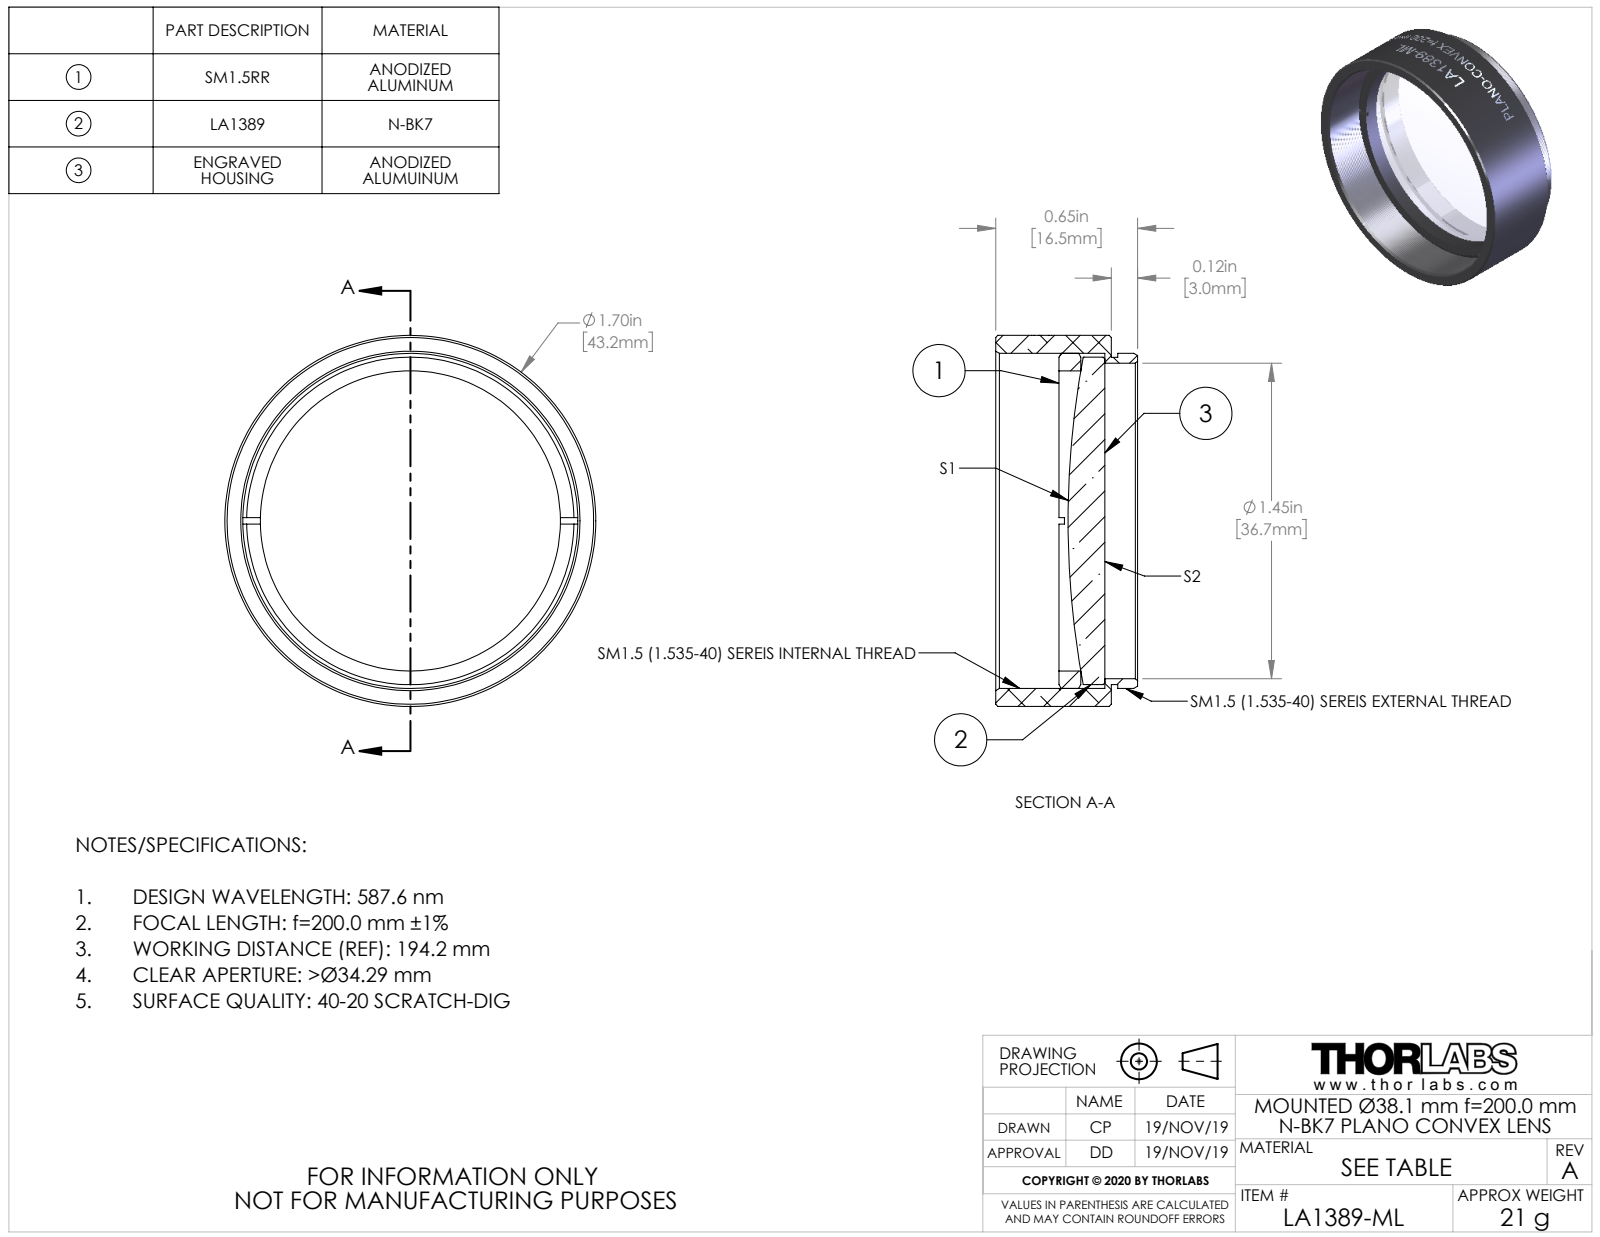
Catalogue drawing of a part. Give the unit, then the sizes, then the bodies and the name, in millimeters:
Units: millimetres
Overall size (bounding box): 43.18 × 43.18 × 16.51
Round holes (diameter × count): ⌀34.92 ×1, ⌀36.7 ×1
Round bosses / shafts (diameter × count): ⌀43.18 ×1, ⌀38.99 ×1, ⌀38.1 ×1, ⌀38.07 ×1
Main face-to-face distances: 0.76, 13.46, 12.7, 3.55, 2.79, 9.91, 6.09, 5.33, 2.54, 7.37
Volume: 8 532 mm³ · Surface area: 8 607 mm²
Bodies: 3 solids, 122 faces (15 planar, 88 cylindrical, 19 other)
Part name (STEP PRODUCT): TTN200694-E0W
STEP written by: SolidWorks 2018 (CONFIG_CONTROL_DESIGN)
